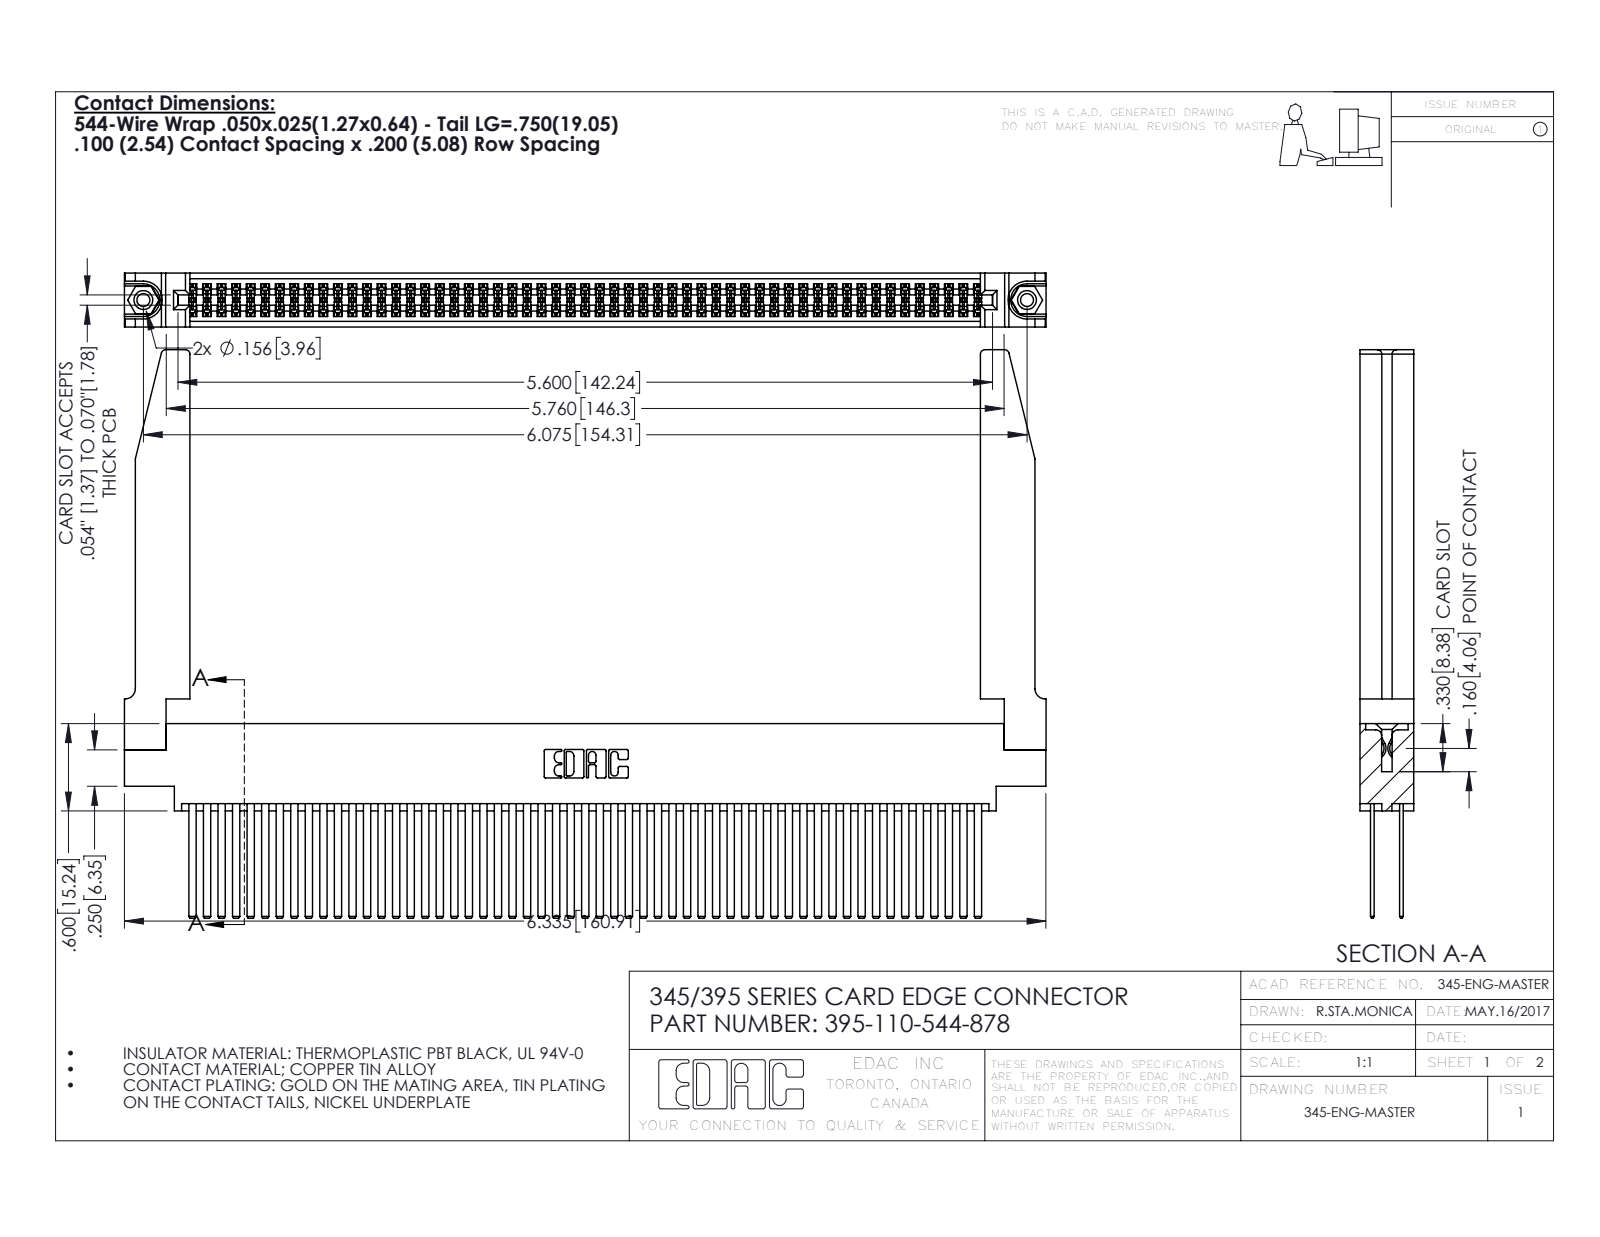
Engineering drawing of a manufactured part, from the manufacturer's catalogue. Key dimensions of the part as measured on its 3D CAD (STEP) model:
Part name (STEP PRODUCT): 345-250-001_345-250-001-102; 345-220-078_345-220-078; 395-110-544-878; 345-292-001_345-293-144 (+1 more)
STEP written by: SolidWorks 2016 (CONFIG_CONTROL_DESIGN)
Units: inches
Bodies: 115 solids, 5204 faces (3416 planar, 1736 cylindrical, 52 other)
Overall size (bounding box): 6.336 × 3.907 × 0.37
Volume: 1.523 in³ · Surface area: 57.59 in²
Round holes (diameter × count): ⌀0.089 ×2, ⌀0.125 ×2, ⌀0.156 ×2, ⌀0.064 ×1
Round bosses / shafts (diameter × count): ⌀0.155 ×2
Partial cylindrical surfaces — rounded edges, fillets, slot ends (radius × count): R0.006 ×165, R0.01 ×22, R0.03 ×8, R0.007 ×6, R0.031 ×6, R0.026 ×3, R0.014 ×2, R0.019 ×2
Main face-to-face distances: 0.072, 0.298, 0.098, 0.272, 0.025, 0.2, 0.37, 0.225, 0.175, 0.148
Hole centre spacings: 0.27, 5.839, 6.075
